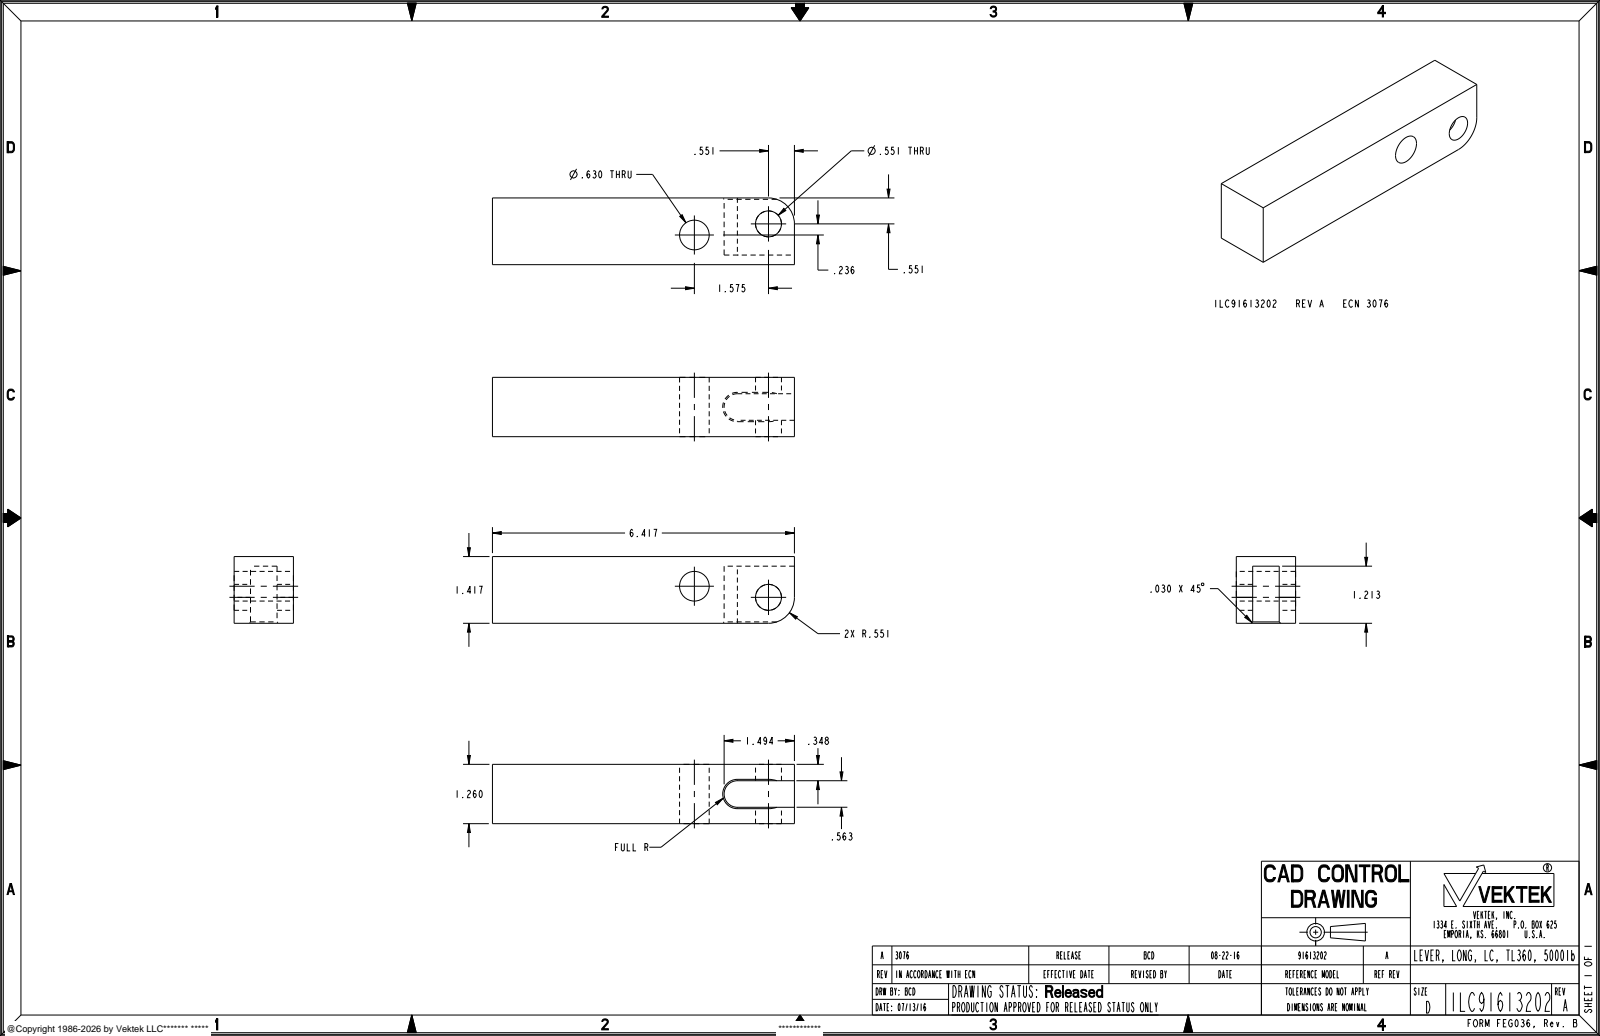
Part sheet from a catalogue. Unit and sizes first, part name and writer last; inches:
Units: inches
Overall size (bounding box): 6.417 × 1.417 × 1.26
Round holes (diameter × count): ⌀0.551 ×1, ⌀0.63 ×1
Partial cylindrical surfaces — rounded edges, fillets, slot ends (radius × count): R0.282 ×1, R0.551 ×1
Main face-to-face distances: 1.26, 1.417, 0.348, 0.912, 0.564, 1.213, 0.204, 6.417
Hole centre spacings: 1.593
Volume: 9.871 in³ · Surface area: 42.91 in²
Bodies: 1 solid, 21 faces (11 planar, 9 cylindrical, 1 other)
Part name (STEP PRODUCT): ILC91613202
STEP written by: PRO/ENGINEER BY PARAMETRIC TECHNOLOGY CORPORATION, 2013320 (AUTOMOTIVE_DESIGN)
